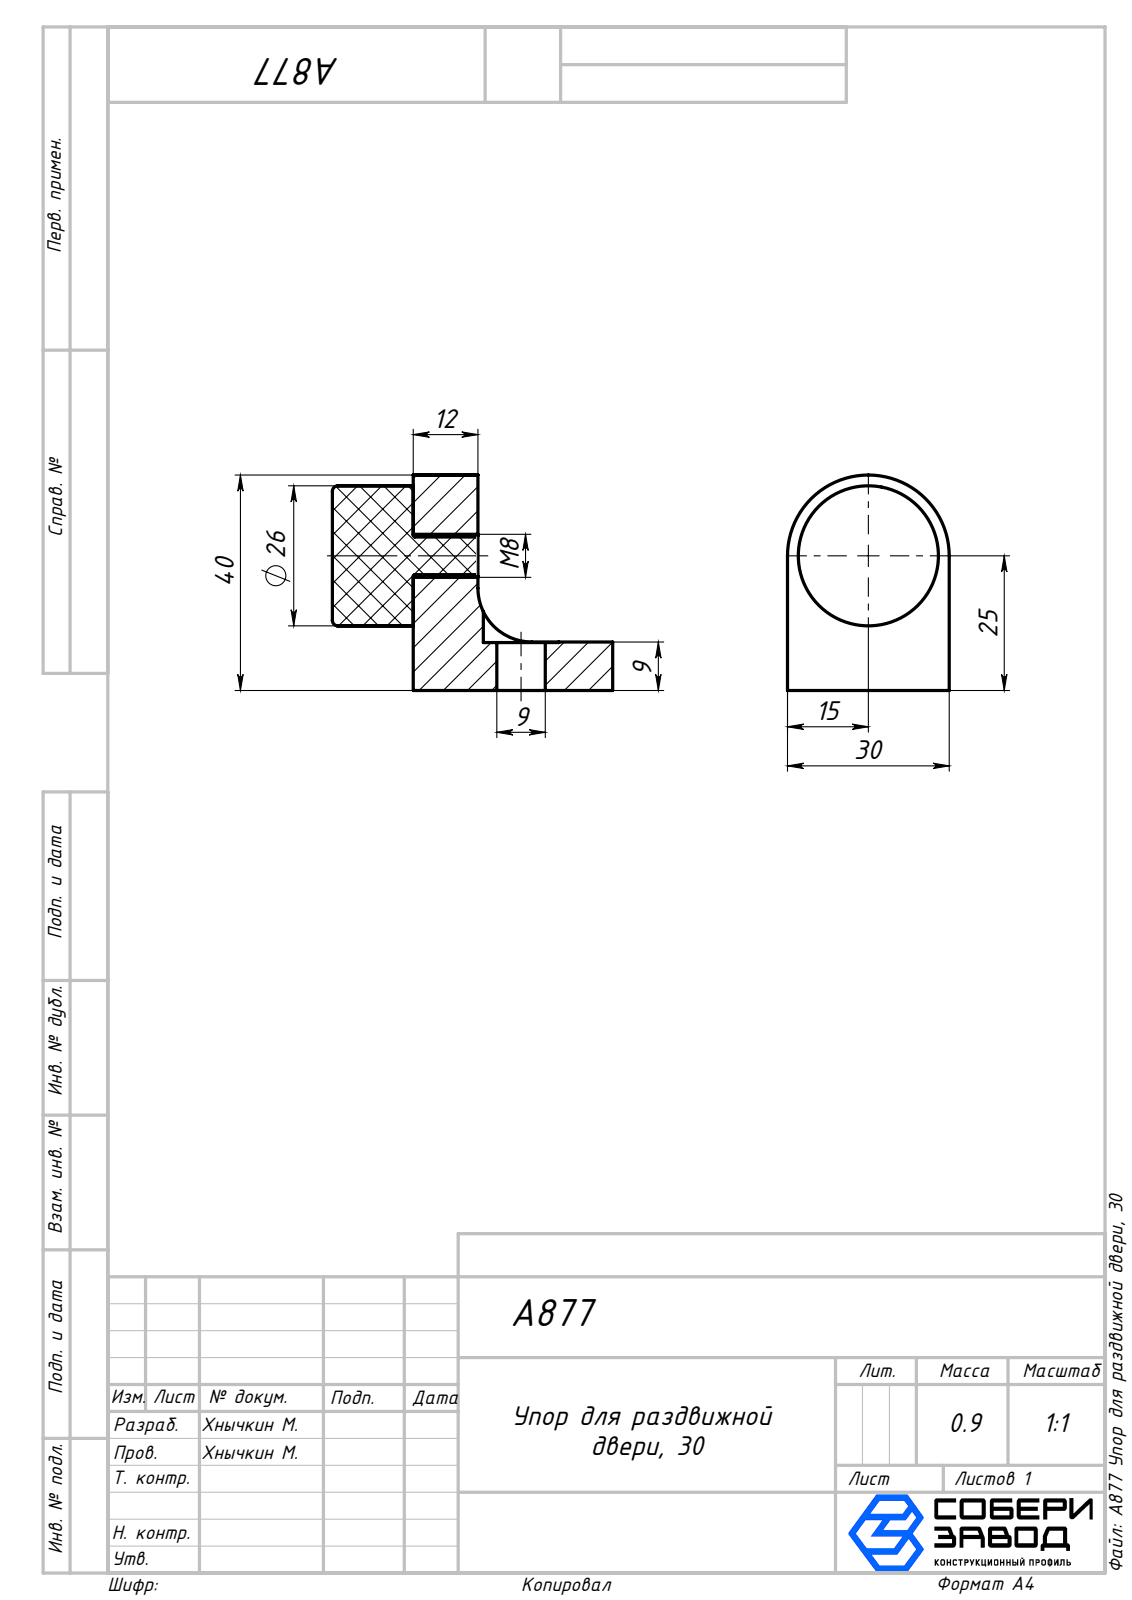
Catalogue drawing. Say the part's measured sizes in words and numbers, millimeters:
The part is named "A877 Ножка_00; A877 Упор для раздвижной двери, 30; A877 Корпус_00". Its 3-D file was written by "SolidWorks 2025 (AUTOMOTIVE_DESIGN)". It is 2 solids with 30 faces: 11 planar, 13 cylindrical and 6 other. Overall it measures 52 by 40 by 30 millimeters. Its volume is 28 014 cubic millimeters and its surface area 8 506 square millimeters. Round holes: 1 of diameter 7, 1 of diameter 9, 1 of diameter 14. Round bosses or shafts: 1 of diameter 26, 1 of diameter 8. Partial cylindrical surfaces (rounded edges, fillets, slot ends): 1 of radius 10, 1 of radius 15. The main face-to-face distances are 30, 12, 15, 27, 9, 52, 37, 25, 8.9.
